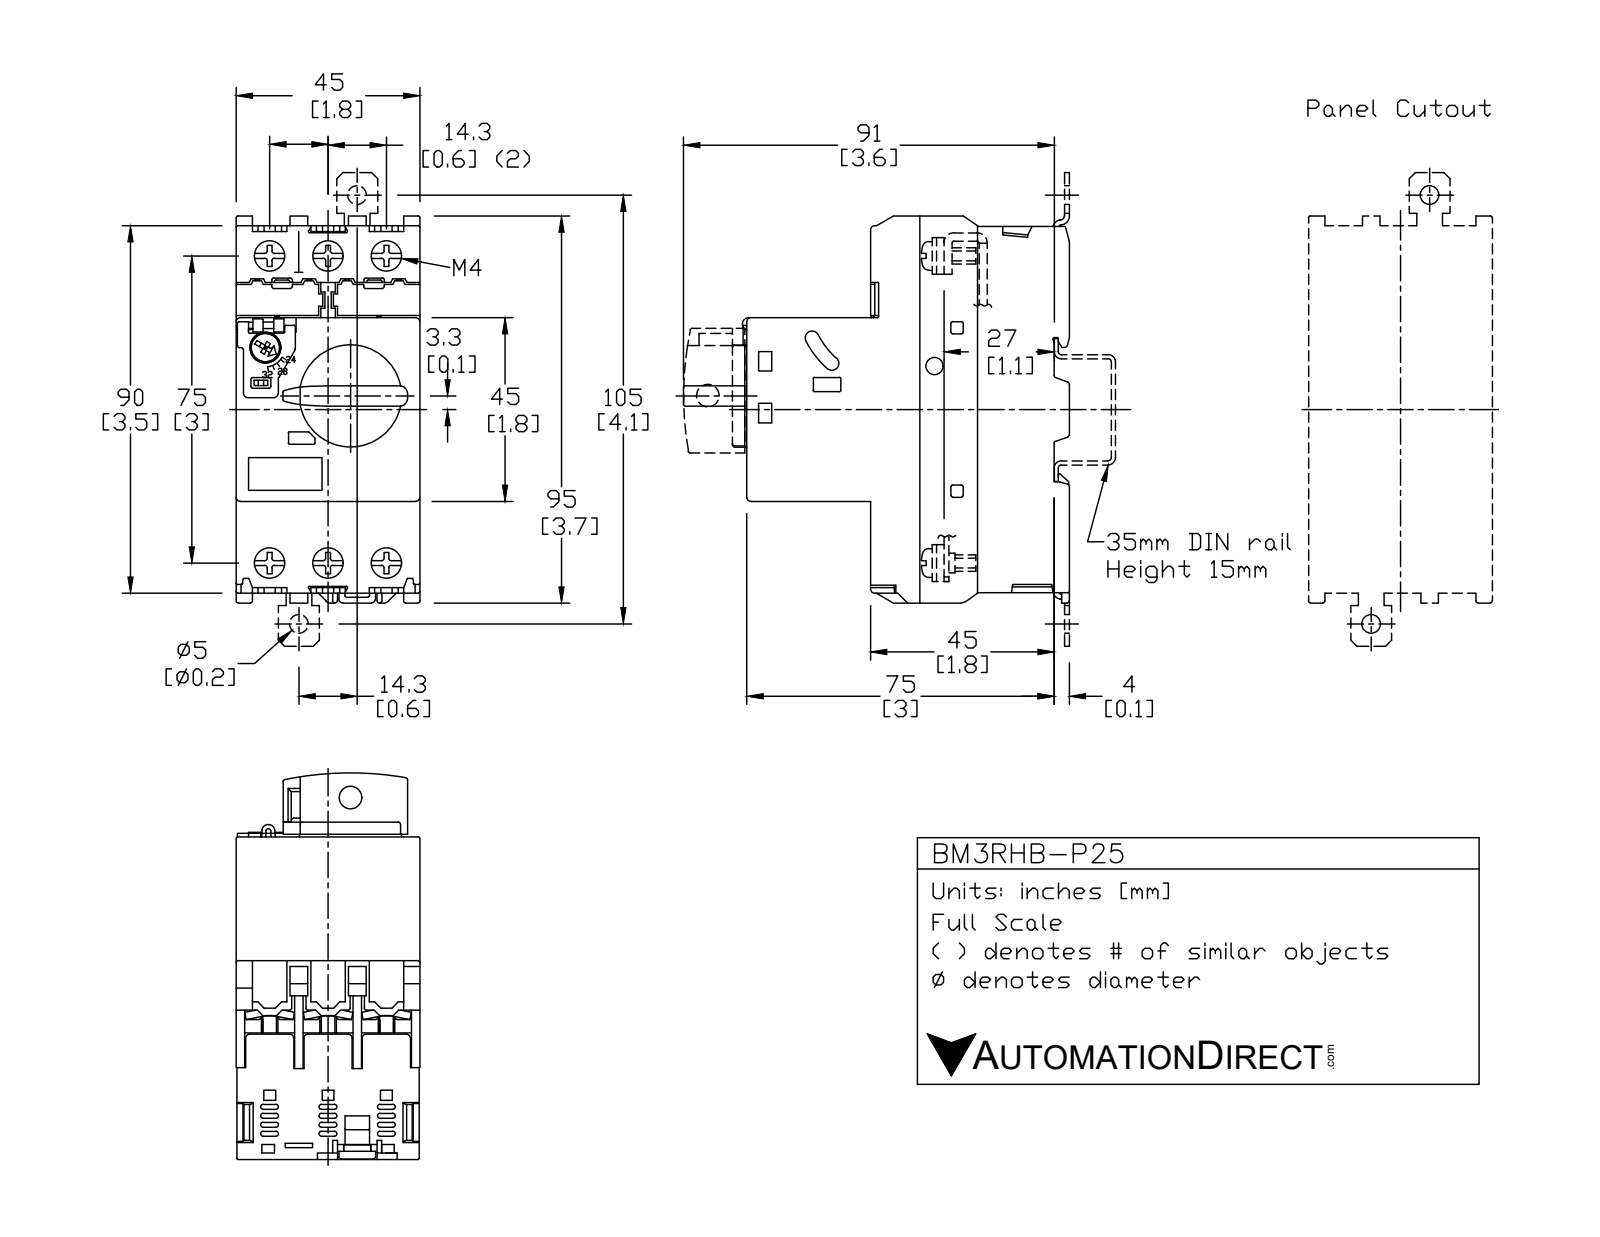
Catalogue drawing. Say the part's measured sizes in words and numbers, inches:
The part is named "BM3RHB-P25". Its 3-D file was written by "SolidWorks 2018 (AUTOMOTIVE_DESIGN)". It is 25 solids with 1294 faces: 964 planar, 327 cylindrical and 3 other. Overall it measures 3.732 by 3.72 by 1.772 inches. Its volume is 14.13 cubic inches and its surface area 88.41 square inches. Round holes: 6 of diameter 0.157, 6 of diameter 0.291, 1 of diameter 0.063, 1 of diameter 0.165, 1 of diameter 0.197, 1 of diameter 0.217, 1 of diameter 0.295. Round bosses or shafts: 6 of diameter 0.236, 1 of diameter 0.984, 1 of diameter 0.276. Partial cylindrical surfaces (rounded edges, fillets, slot ends): 67 of radius 0.02, 24 of radius 0.024, 14 of radius 0.079, 12 of radius 0.012, 8 of radius 0.039, 8 of radius 0.098, 6 of radius 0.008, 2 of radius 0.059. The main face-to-face distances are 1.772, 1.441, 1.669, 3.11, 0.882, 2.654, 0.118, 0.65, 0.791, 0.472. The hole center spacings are 0.563, 3.006, 2.953, 1.126, 3.16, 0.883, 0.941, 1.068.
